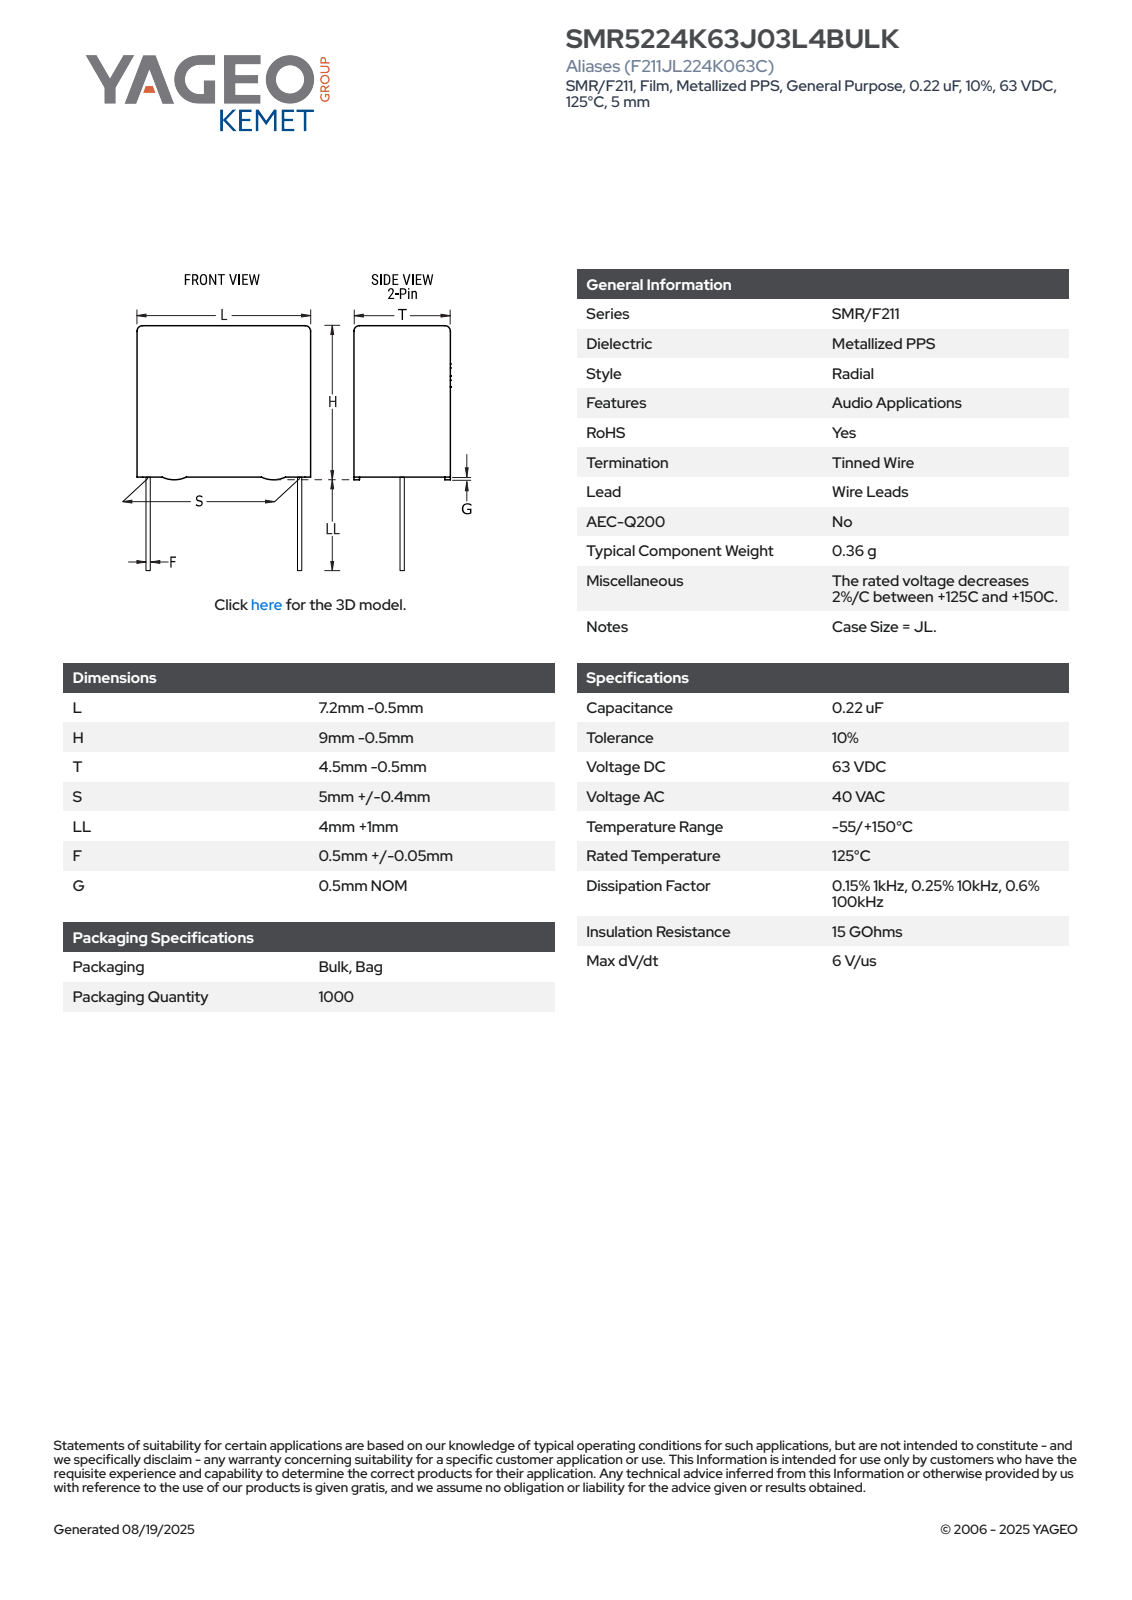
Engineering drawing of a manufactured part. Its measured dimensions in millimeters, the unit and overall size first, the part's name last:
Units: millimetres
Overall size (bounding box): 13.5 × 6.7 × 4
Round bosses / shafts (diameter × count): ⌀0.55 ×2
Partial cylindrical surfaces — rounded edges, fillets, slot ends (radius × count): R0.5 ×4
Main face-to-face distances: 4, 6.7, 8, 3.77, 3.54, 0.5, 8.5, 2.49, 5, 5.5
Volume: 216 mm³ · Surface area: 249 mm²
Bodies: 4 solids, 89 faces (81 planar, 8 cylindrical, 0 other)
Part name (STEP PRODUCT): CFR_RBG_7.2X9X4.5_L6.7H8.5T4S5LL5F0.55G0.5
STEP written by: SolidWorks 2021 (AUTOMOTIVE_DESIGN)
